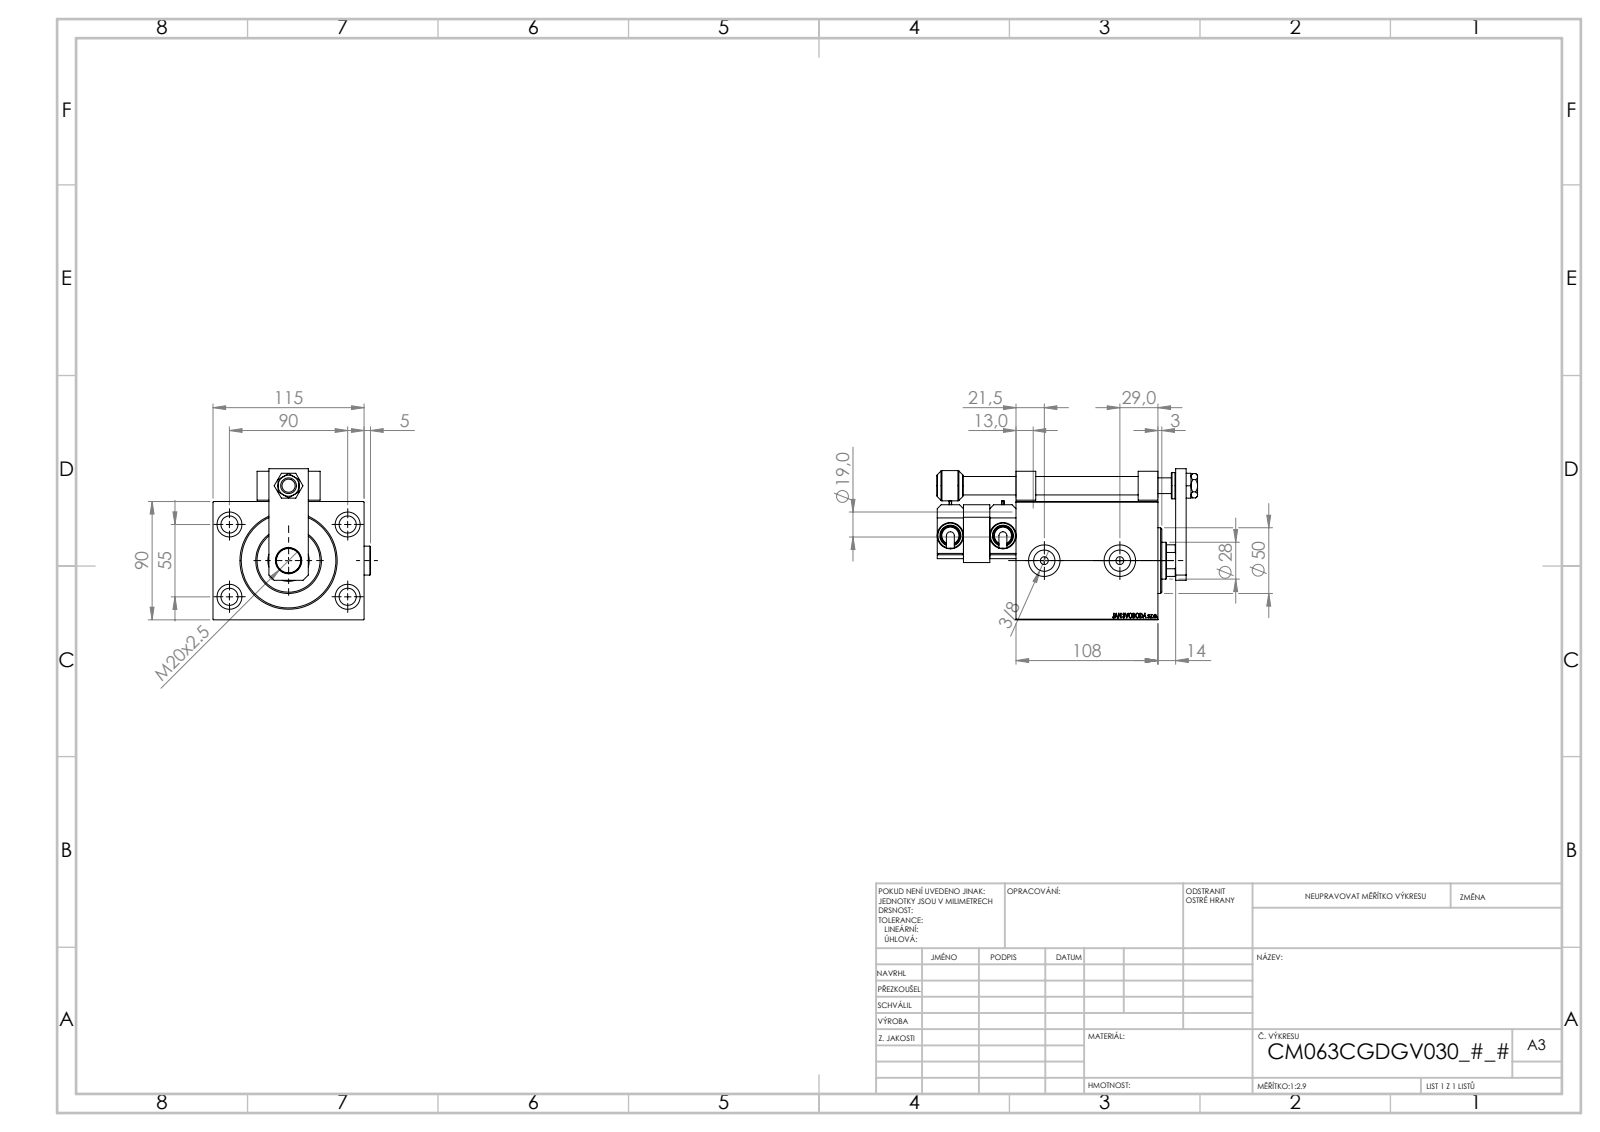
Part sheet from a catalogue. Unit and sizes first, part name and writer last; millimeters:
Units: millimetres
Overall size (bounding box): 198.5 × 119.9 × 115
Round holes (diameter × count): ⌀13 ×5, ⌀4 ×4, ⌀8 ×4, ⌀19 ×4, ⌀6 ×2, ⌀16.17 ×2, ⌀24 ×2, ⌀12 ×1, ⌀14 ×1, ⌀18.5 ×1, ⌀20 ×1, ⌀28 ×1
Round bosses / shafts (diameter × count): ⌀20 ×3, ⌀22 ×2, ⌀16 ×2, ⌀14 ×2, ⌀6 ×2, ⌀50 ×1, ⌀23 ×1
Partial cylindrical surfaces — rounded edges, fillets, slot ends (radius × count): R3 ×1, R13.5 ×1
Main face-to-face distances: 90, 115, 20, 108, 17.5, 37.5, 90.5, 40, 13.5, 77.5
Hole centre spacings: 52.74, 20, 53.81, 55, 90, 93, 95.13, 95.74
Volume: 1 141 000 mm³ · Surface area: 191 450 mm²
Bodies: 16 solids, 1144 faces (555 planar, 136 cylindrical, 453 other)
Part name (STEP PRODUCT): TYC_P; SWITCH_P_FRONT_BACK; MIDDLE; NUT_D19_P (+7 more)
STEP written by: SolidWorks 2019 (CONFIG_CONTROL_DESIGN)
